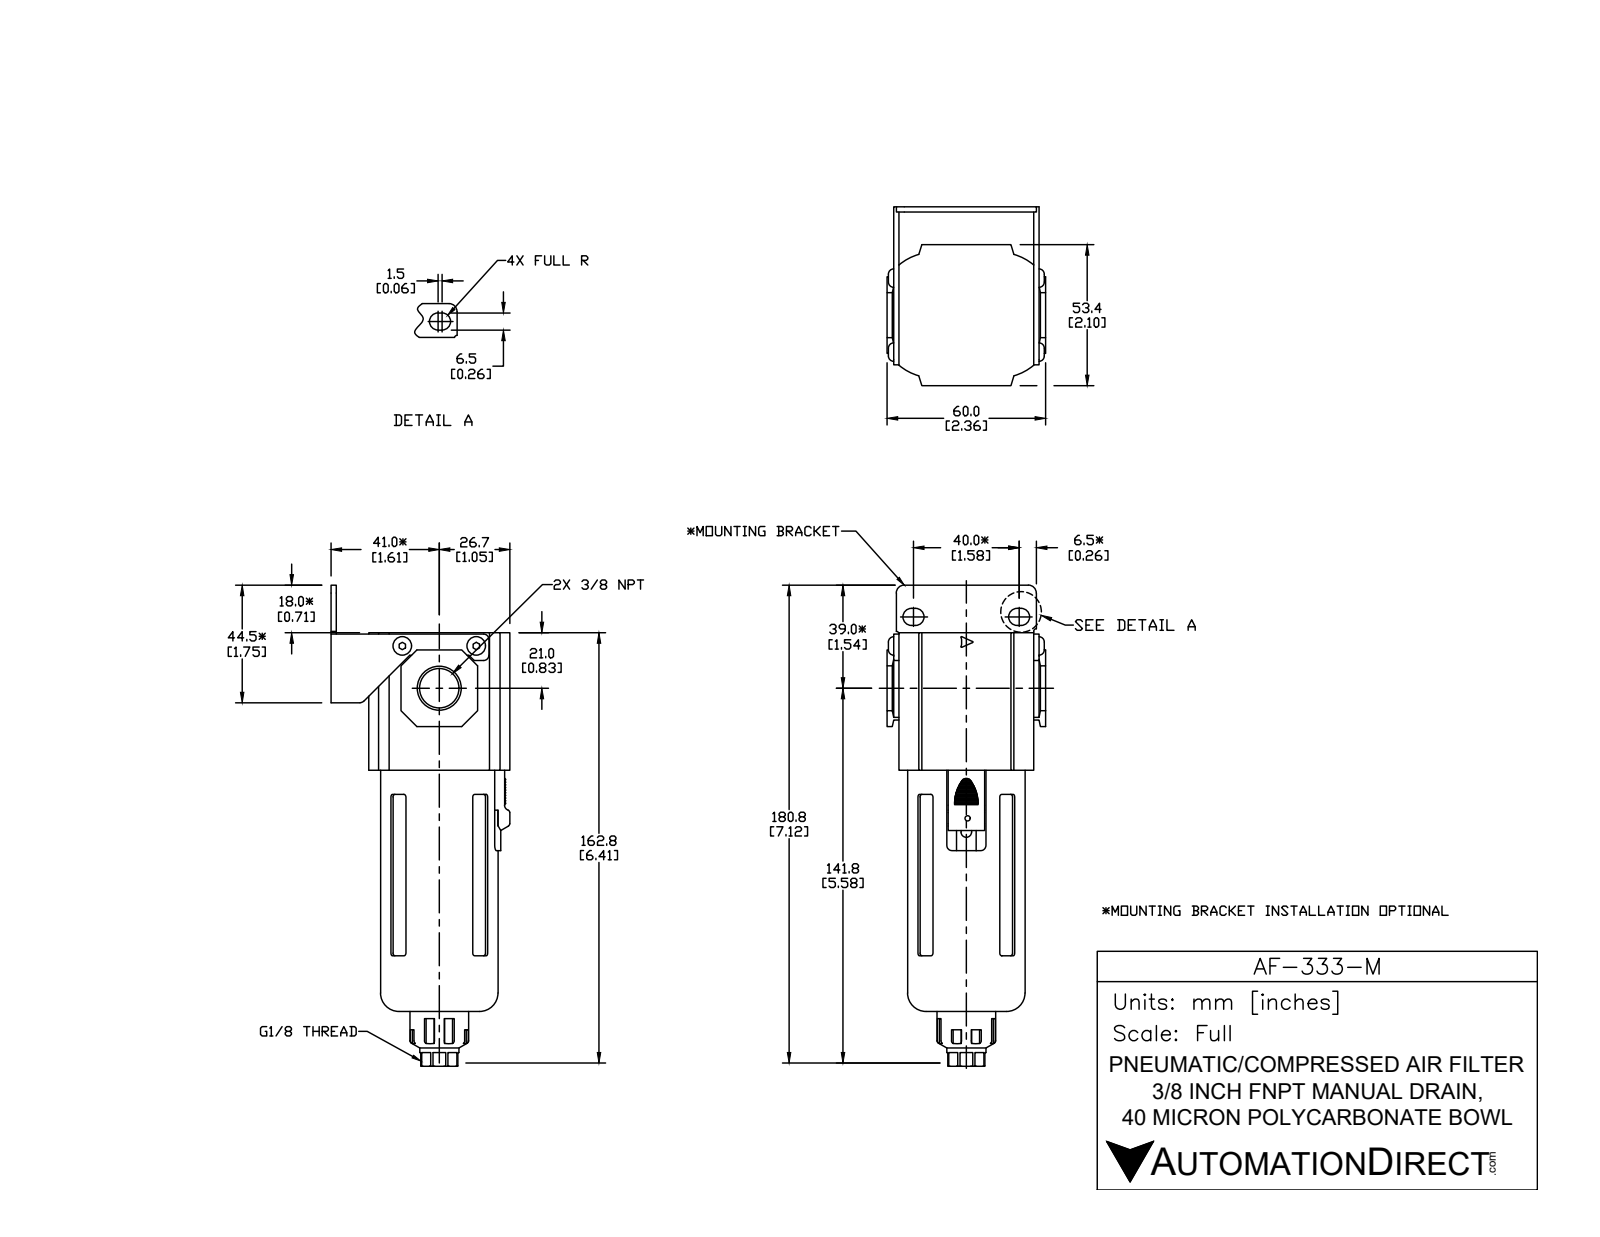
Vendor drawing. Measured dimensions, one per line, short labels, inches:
name: AF-333-M
written by: SolidWorks 2015 (CONFIG_CONTROL_DESIGN)
unit: in
bodies: 9 solids, 394 faces (246 planar, 94 cylindrical, 54 other)
size: 7.177 × 2.665 × 2.362
volume: 12.4 in³; area: 94.46 in²
holes: 2× ⌀0.134, 1× ⌀0.337, 1× ⌀0.562, 1× ⌀1.417, 1× ⌀1.764
bosses: 1× ⌀1.751, 1× ⌀1.024, 1× ⌀0.876, 1× ⌀0.583
rounds: 18× R0.039, 8× R0.079, 8× R0.374, 6× R0.02, 4× R0.012, 4× R0.128, 4× R0.787, 3× R0.008
face distances: 0.079, 2.008, 2.087, 0.098, 0.484, 2.665, 2.587, 0.563, 2.102, 2.185
hole spacings: 0.829, 0.845, 1.102
